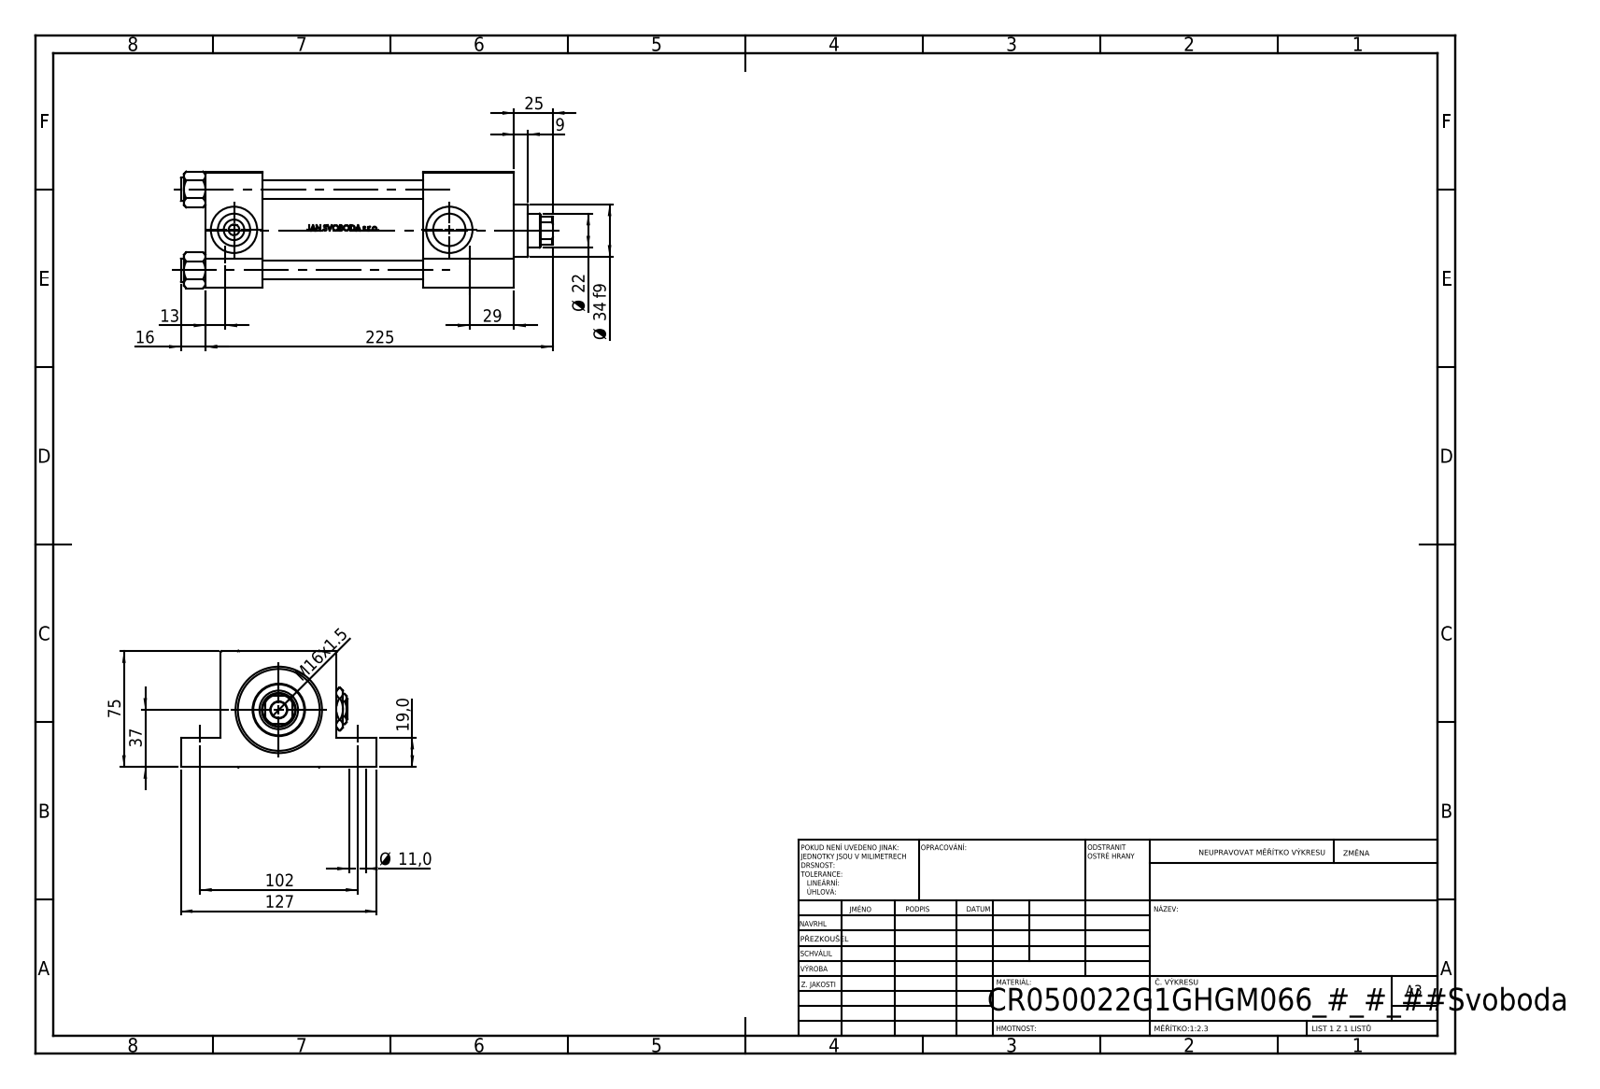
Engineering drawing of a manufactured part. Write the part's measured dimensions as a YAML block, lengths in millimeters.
part_name: "V215CR_VCP_G; V215_VC_A; NUT_M5_G; V215CR_G_Body (+2 more)"
step_written_by: "SolidWorks 2019 (CONFIG_CONTROL_DESIGN)"
units: millimeters
bodies: {solids: 12, faces: 1134, planar: 454, cylindrical: 128, other: 552}
overall_size: [241, 127, 75.54]
volume: 813677
surface_area: 186738
round_holes:
  - {diameter: 11, count: 4}
  - {diameter: 12, count: 4}
  - {diameter: 7, count: 2}
  - {diameter: 20.96, count: 2}
  - {diameter: 30, count: 2}
  - {diameter: 10.5, count: 1}
  - {diameter: 22, count: 1}
  - {diameter: 25, count: 1}
  - {diameter: 41, count: 1}
  - {diameter: 50, count: 1}
  - {diameter: 53, count: 1}
round_bosses_or_shafts:
  - {diameter: 15, count: 4}
  - {diameter: 56, count: 1}
  - {diameter: 34, count: 1}
partial_cylinders:
  - {radius: 10.5, count: 1}
face_to_face_distances: [75, 37, 200, 163, 19, 56, 141, 104, 59, 26]
hole_center_spacings: [52.3, 36.63, 37.34, 73.96, 102, 158, 188.06, 139.5]
